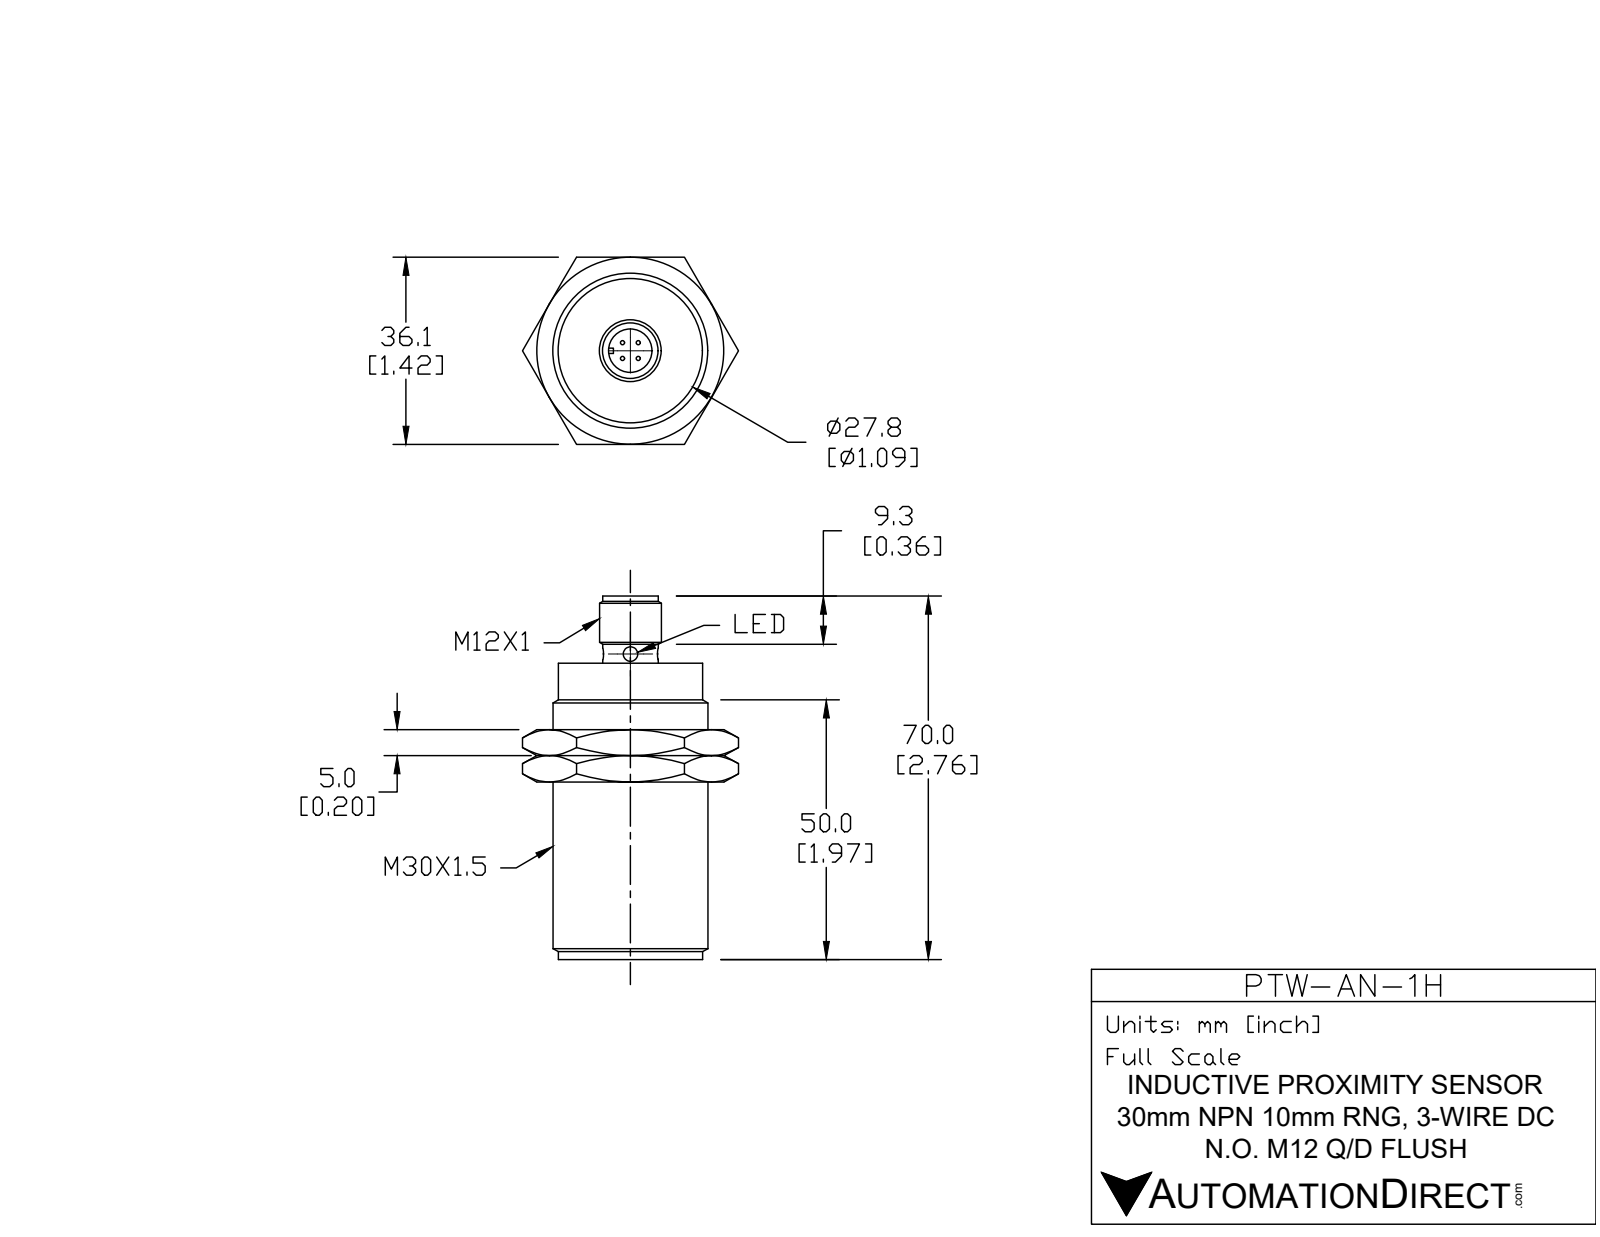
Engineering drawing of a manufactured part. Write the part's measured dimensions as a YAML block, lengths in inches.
part_name: "PTW-AN-1H"
step_written_by: "SolidWorks 2017 (AUTOMOTIVE_DESIGN)"
units: inches
bodies: {solids: 3, faces: 97, planar: 20, cylindrical: 31, other: 46}
overall_size: [2.756, 1.637, 1.417]
volume: 2.748
surface_area: 17.21
round_holes:
  - {diameter: 0.059, count: 2}
  - {diameter: 0.354, count: 1}
  - {diameter: 1.084, count: 1}
  - {diameter: 1.117, count: 1}
round_bosses_or_shafts:
  - {diameter: 1.181, count: 1}
  - {diameter: 0.472, count: 1}
  - {diameter: 0.412, count: 1}
partial_cylinders:
  - {radius: 0.228, count: 1}
face_to_face_distances: [0.197, 0.984, 1.417, 1.26, 2.244, 1.457, 0.787, 1.063, 0.394, 1.181]
